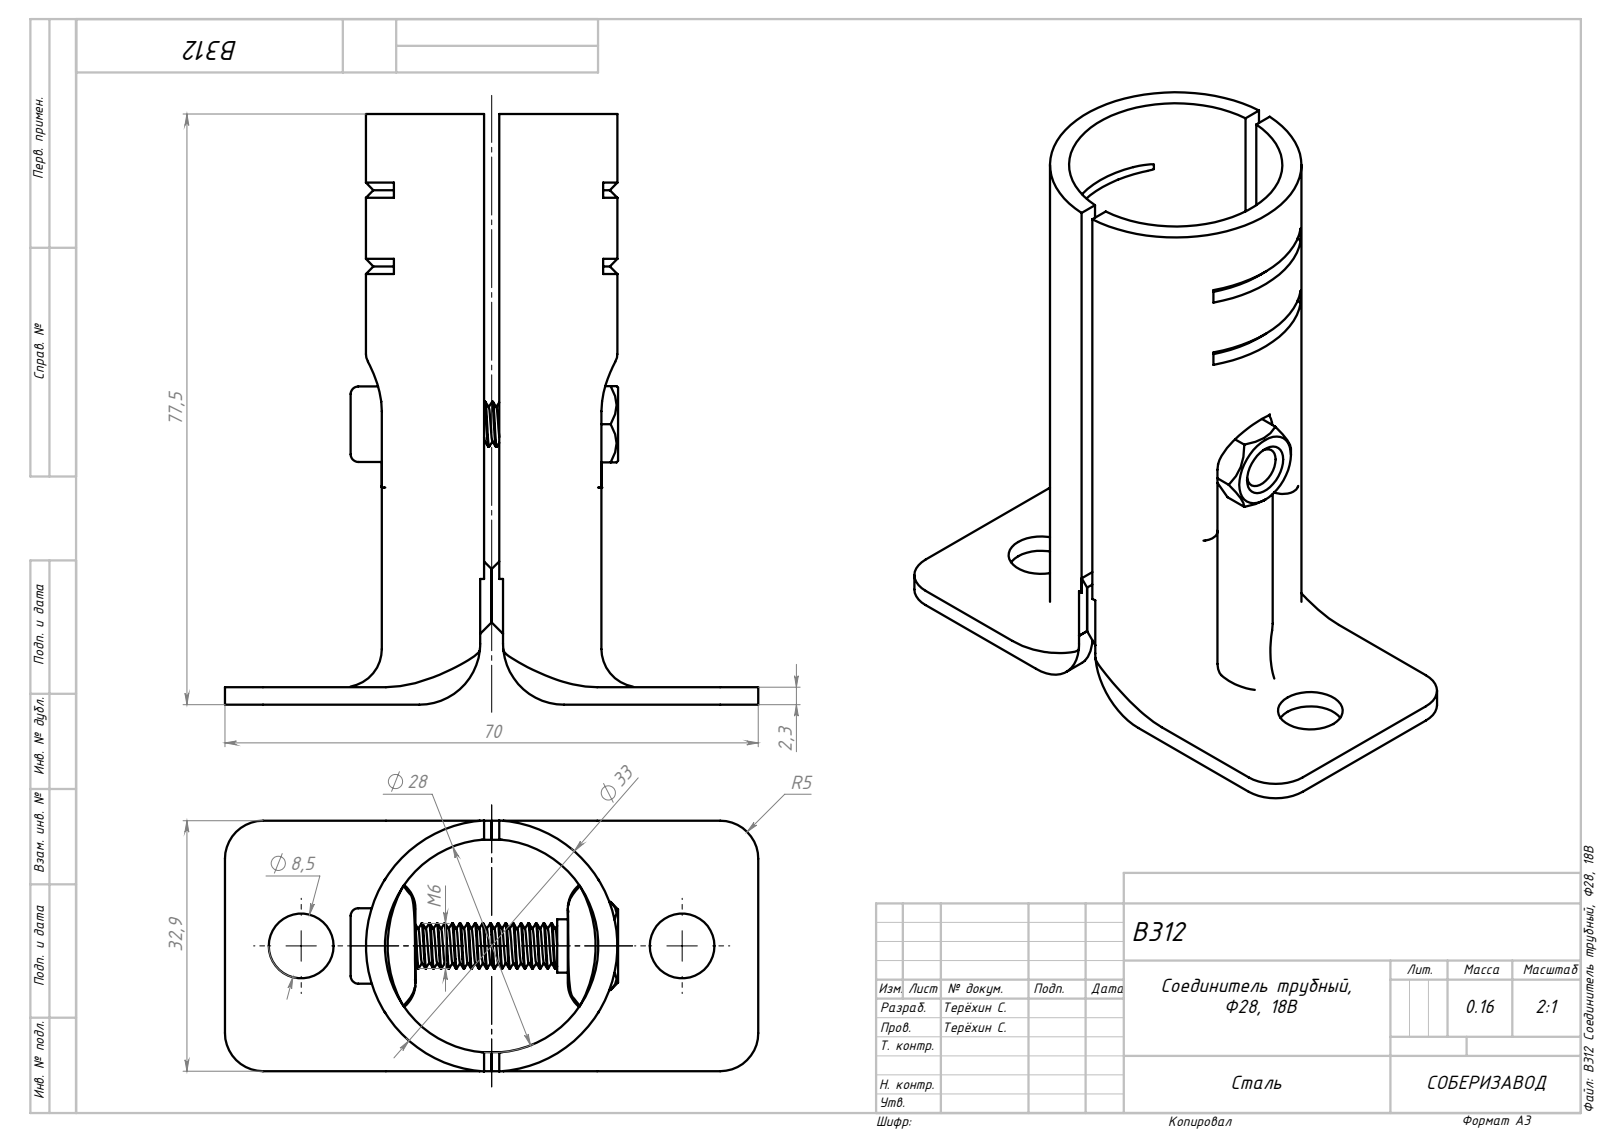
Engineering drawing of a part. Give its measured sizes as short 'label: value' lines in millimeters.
name: B312 Соединитель трубный, Ф28, 18B
written by: SolidWorks 2022 (AUTOMOTIVE_DESIGN)
unit: mm
bodies: 4 solids, 277 faces (88 planar, 96 cylindrical, 93 other)
size: 77.5 × 70 × 32.94
volume: 22 528 mm³; area: 20 086 mm²
holes: 2× ⌀8.5, 1× ⌀5.3, 1× ⌀7.3, 1× ⌀28
bosses: 1× ⌀33, 1× ⌀9.9, 1× ⌀7, 1× ⌀5.9
rounds: 6× R0.3, 6× R4, 4× R5, 2× R3, 2× R8, 2× R16.15, 1× R5.5
face distances: 2.3, 22.5, 2.5, 13.5, 11, 11.5, 9, 25, 20, 2
hole spacings: 25, 50
